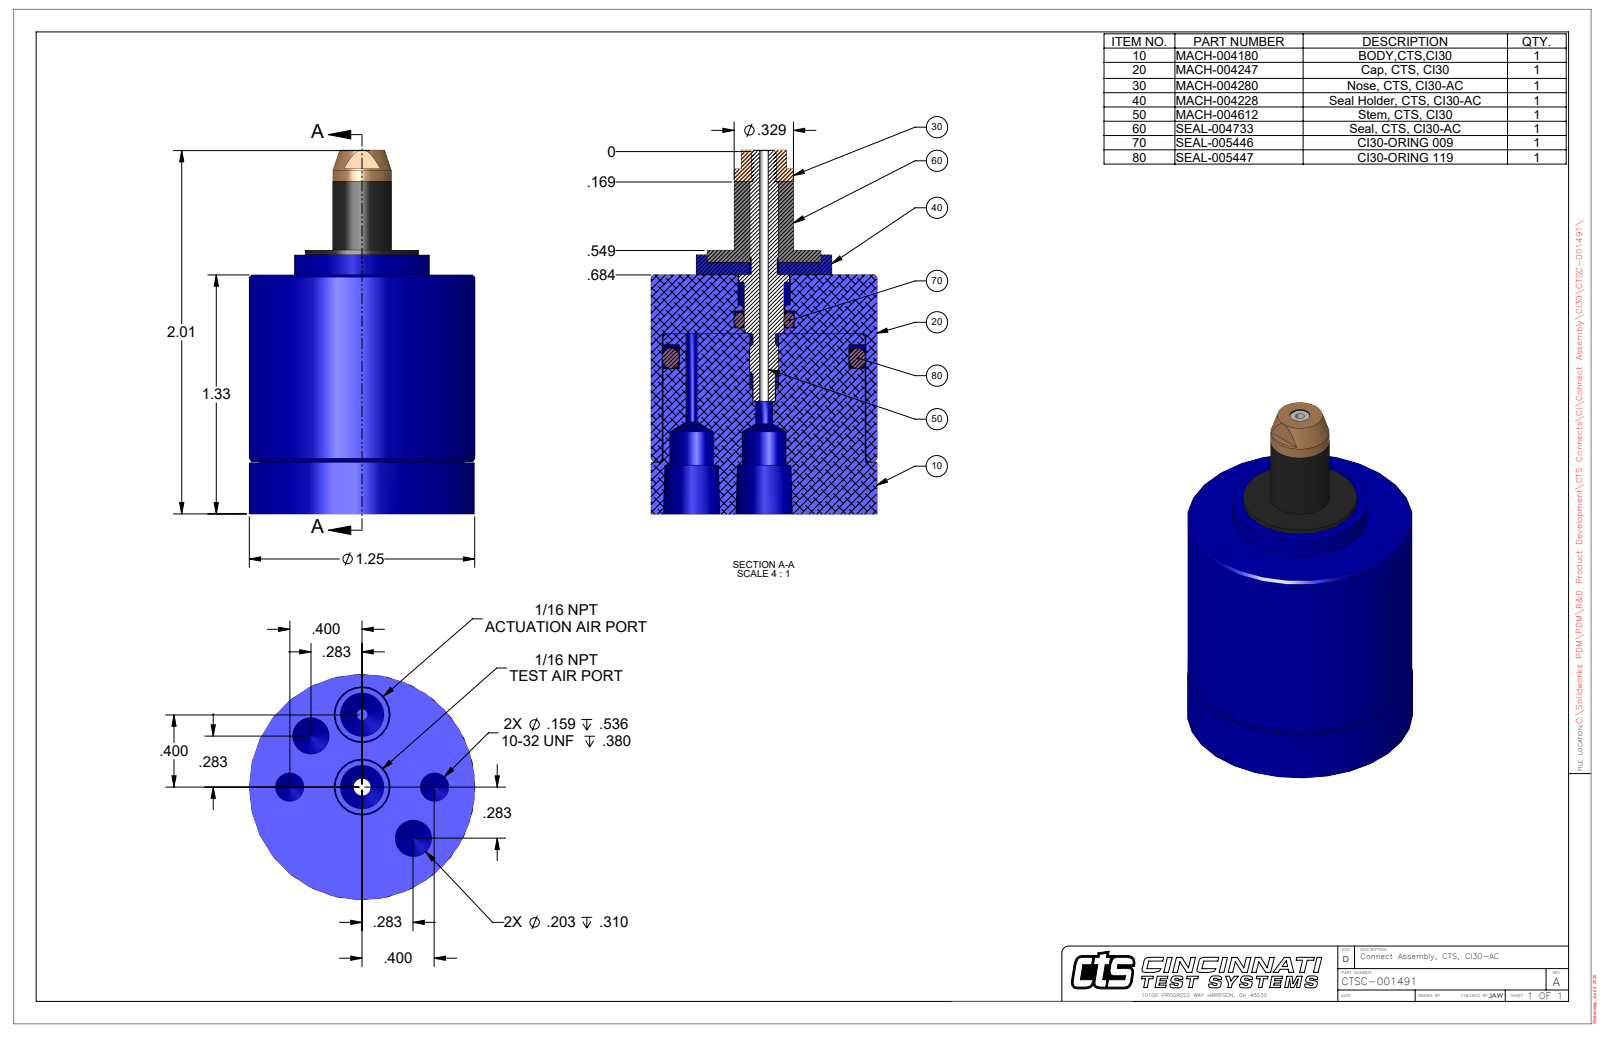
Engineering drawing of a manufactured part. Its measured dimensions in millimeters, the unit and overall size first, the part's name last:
Units: millimetres
Overall size (bounding box): 51.2 × 31.8 × 31.8
Round holes (diameter × count): ⌀4 ×2, ⌀5.2 ×2, ⌀6.1 ×2, ⌀1.3 ×1, ⌀1.6 ×1, ⌀2.4 ×1, ⌀2.9 ×1, ⌀7.3 ×1, ⌀28.6 ×1
Round bosses / shafts (diameter × count): ⌀31.8 ×1, ⌀28.3 ×1, ⌀19.1 ×1, ⌀16 ×1, ⌀8.4 ×1, ⌀8.3 ×1, ⌀7 ×1
Main face-to-face distances: 33.7, 37.1, 3.4, 7.3, 26.4, 29.8, 7.4, 26.3, 29.7, 36.4
Hole centre spacings: 7.8, 10.2, 18.8, 10.2, 14.4, 20.3, 20.3
Volume: 26 430 mm³ · Surface area: 8 581 mm²
Bodies: 1 solid, 93 faces (24 planar, 40 cylindrical, 29 other)
Part name (STEP PRODUCT): CTSC-001491
STEP written by: SolidWorks 2023 (AUTOMOTIVE_DESIGN)
